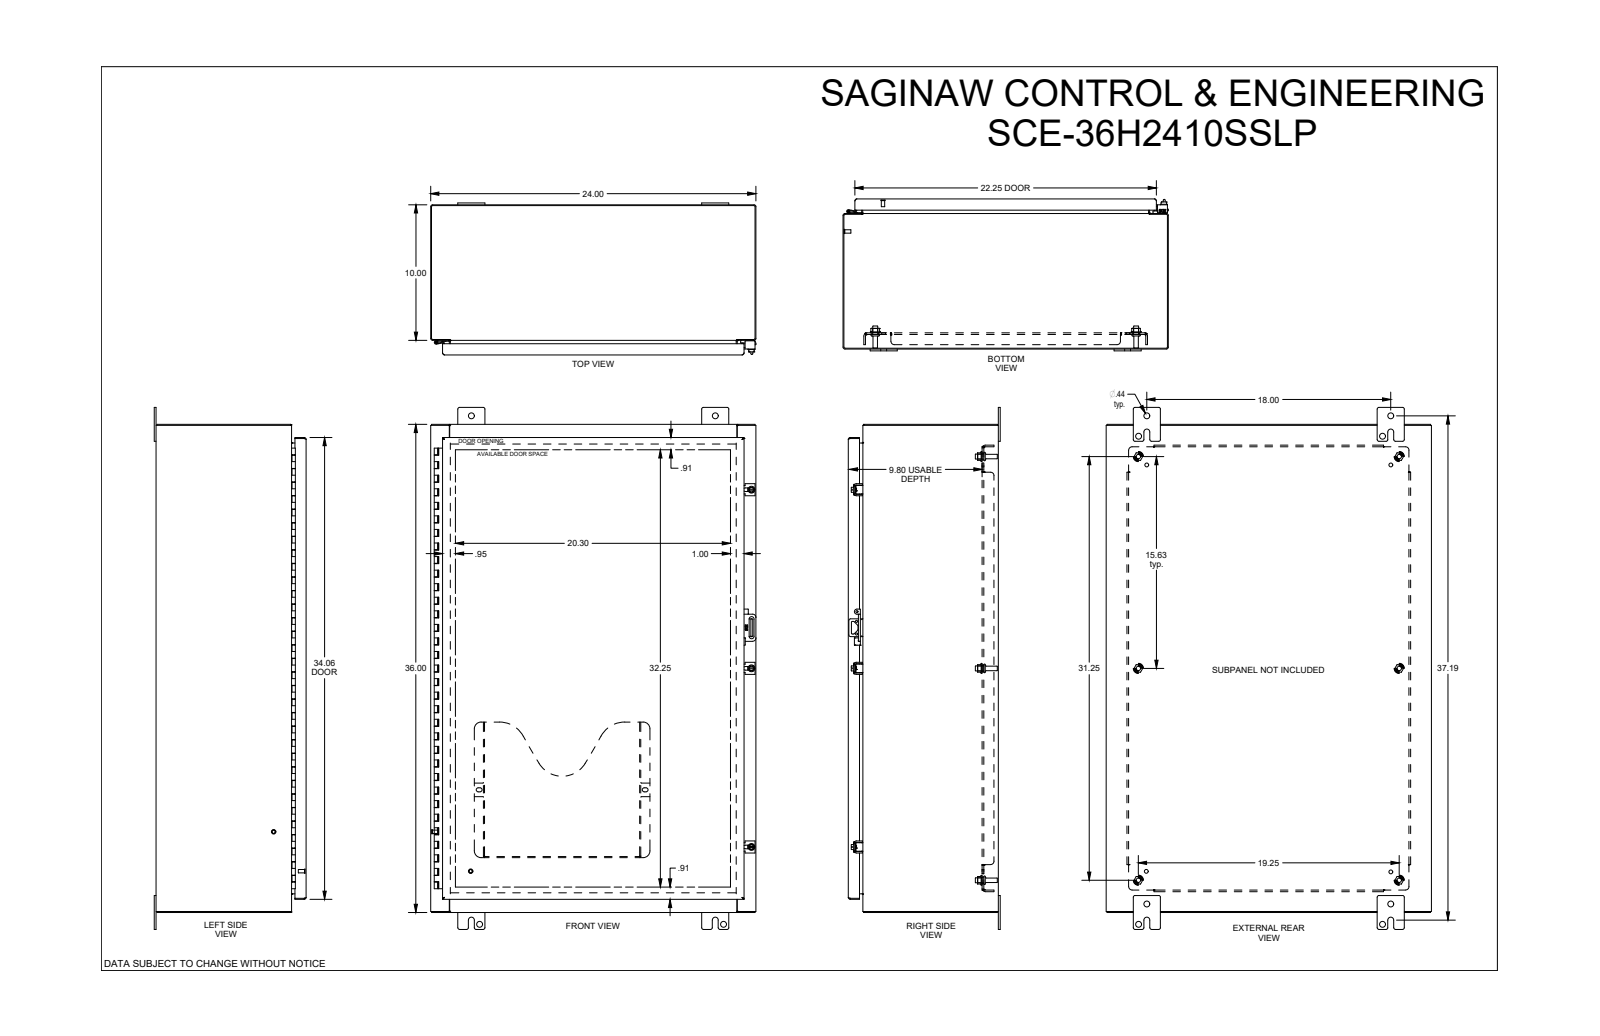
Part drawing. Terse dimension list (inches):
name: SCE-36H2410SSLP
written by: SolidWorks 2019 (CONFIG_CONTROL_DESIGN)
unit: in
bodies: 0 solids, 4019 faces (1647 planar, 844 cylindrical, 1528 other)
size: 38.5 × 24 × 11.208
holes: 8× ⌀0.437, 6× ⌀0.25, 6× ⌀0.367, 6× ⌀0.5, 5× ⌀0.19, 5× ⌀0.193, 4× ⌀0.281, 3× ⌀0.203, 2× ⌀0.16, 1× ⌀0.13, 1× ⌀0.132
bosses: 8× ⌀0.248, 6× ⌀0.563, 6× ⌀0.366, 6× ⌀0.332, 5× ⌀0.256, 5× ⌀0.188, 4× ⌀0.25, 3× ⌀0.507
rounds: 160× R0.01, 44× R0.015, 36× R0.029, 29× R0.06, 27× R0.03, 27× R0.125, 22× R0.04, 14× R0.07
face distances: 0.075, 0.075, 10.998, 10.923, 1.2, 9.873, 11.073, 10.998, 23.925, 9.923
hole spacings: 1.619, 18, 36, 40.249, 0.515, 7.875, 7.875, 15.019
